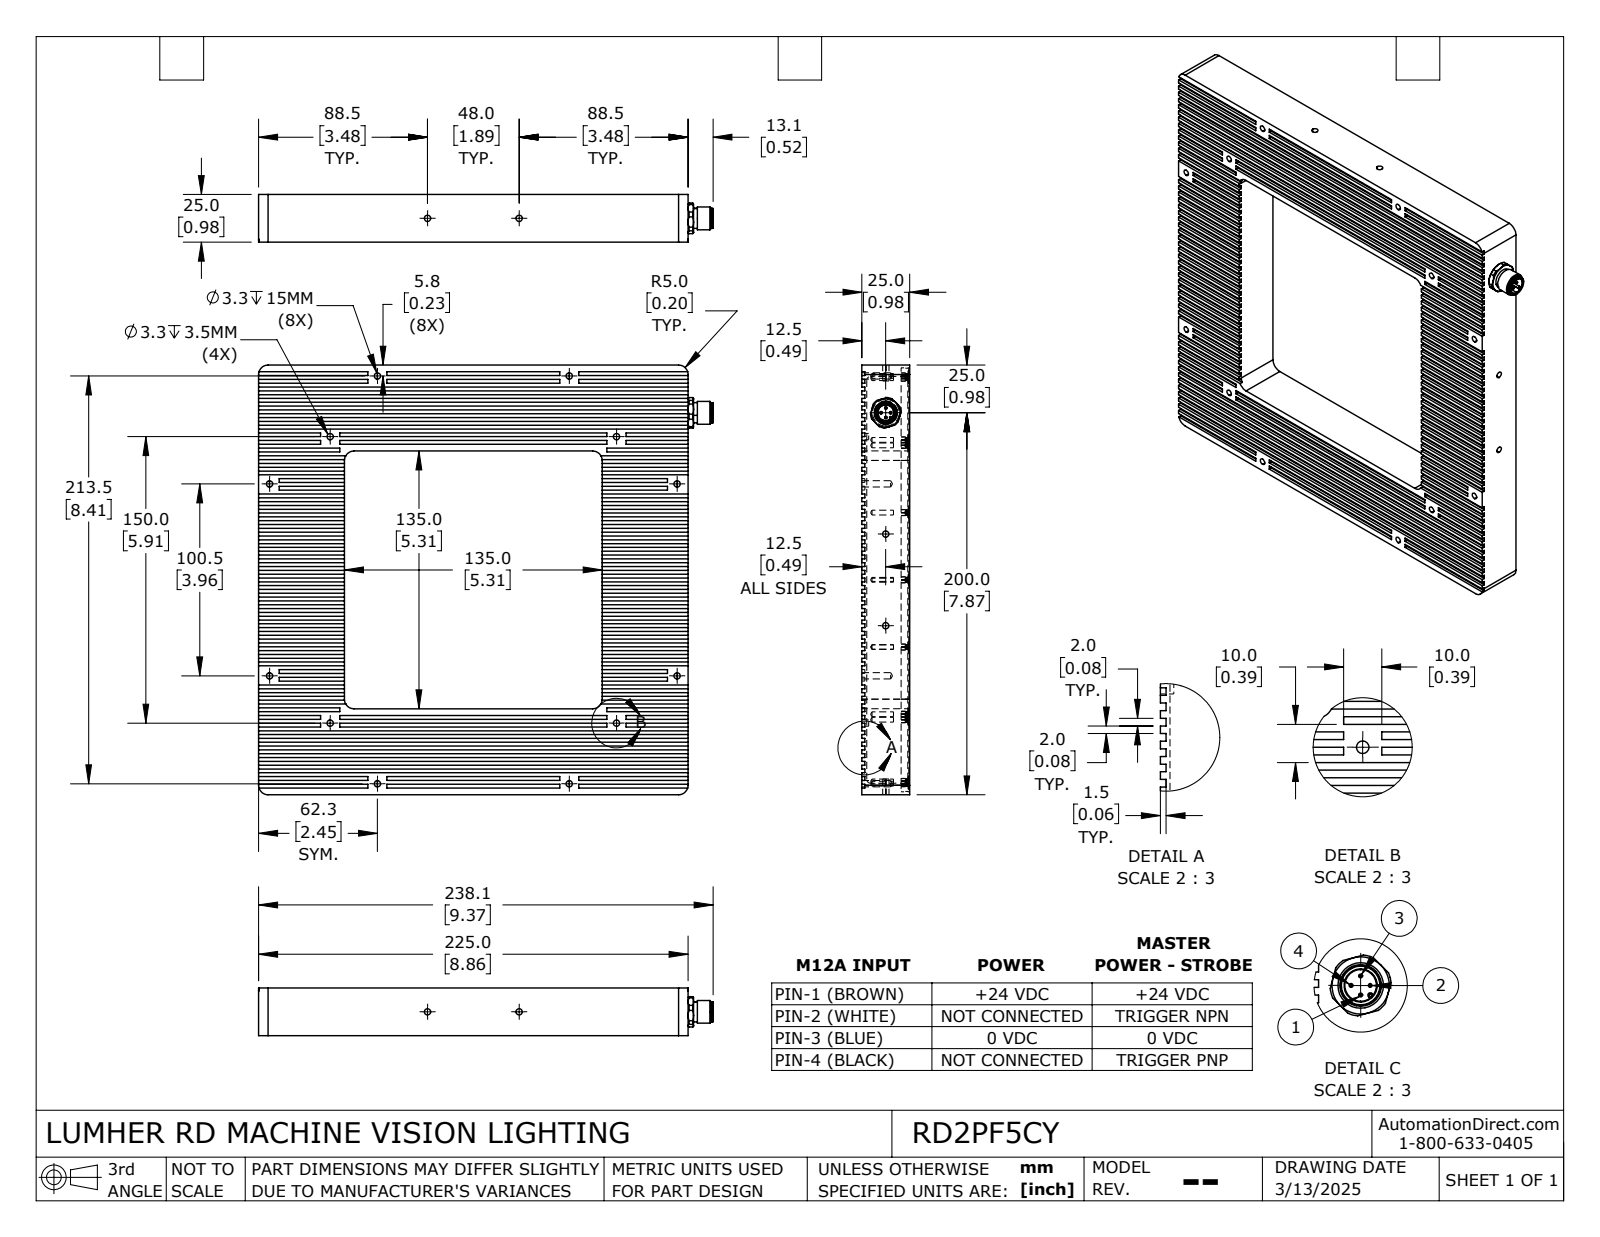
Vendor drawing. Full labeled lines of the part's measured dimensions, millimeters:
Part name (STEP PRODUCT): RD2PF5CY
STEP written by: SolidWorks 2024 (AUTOMOTIVE_DESIGN)
Units: millimetres
Bodies: 1 solid, 3276 faces (670 planar, 1729 cylindrical, 877 other)
Overall size (bounding box): 238.1 × 225 × 25
Volume: 766 576 mm³ · Surface area: 145 055 mm²
Round holes (diameter × count): ⌀3.2 ×40, ⌀2.5 ×38, ⌀3.3 ×16, ⌀1.45 ×4, ⌀8.3 ×1, ⌀9.4 ×1, ⌀11 ×1, ⌀12.2 ×1
Round bosses / shafts (diameter × count): ⌀5.6 ×40, ⌀3 ×40, ⌀0.8 ×40, ⌀1.4 ×4, ⌀1 ×4, ⌀11.91 ×1, ⌀11.9 ×1, ⌀10.6 ×1
Partial cylindrical surfaces — rounded edges, fillets, slot ends (radius × count): R0.57 ×480, R0.25 ×240, R1.02 ×40, R5 ×8, R2 ×4, R3.3 ×4, R3.5 ×4, R6.5 ×4
Main face-to-face distances: 1.5, 24.5, 180, 23, 45, 43.5, 135, 225, 43.3, 1.7
Hole centre spacings: 40.26, 129.21, 166.86, 183.43, 220.73, 55.34, 155.83, 183.15
